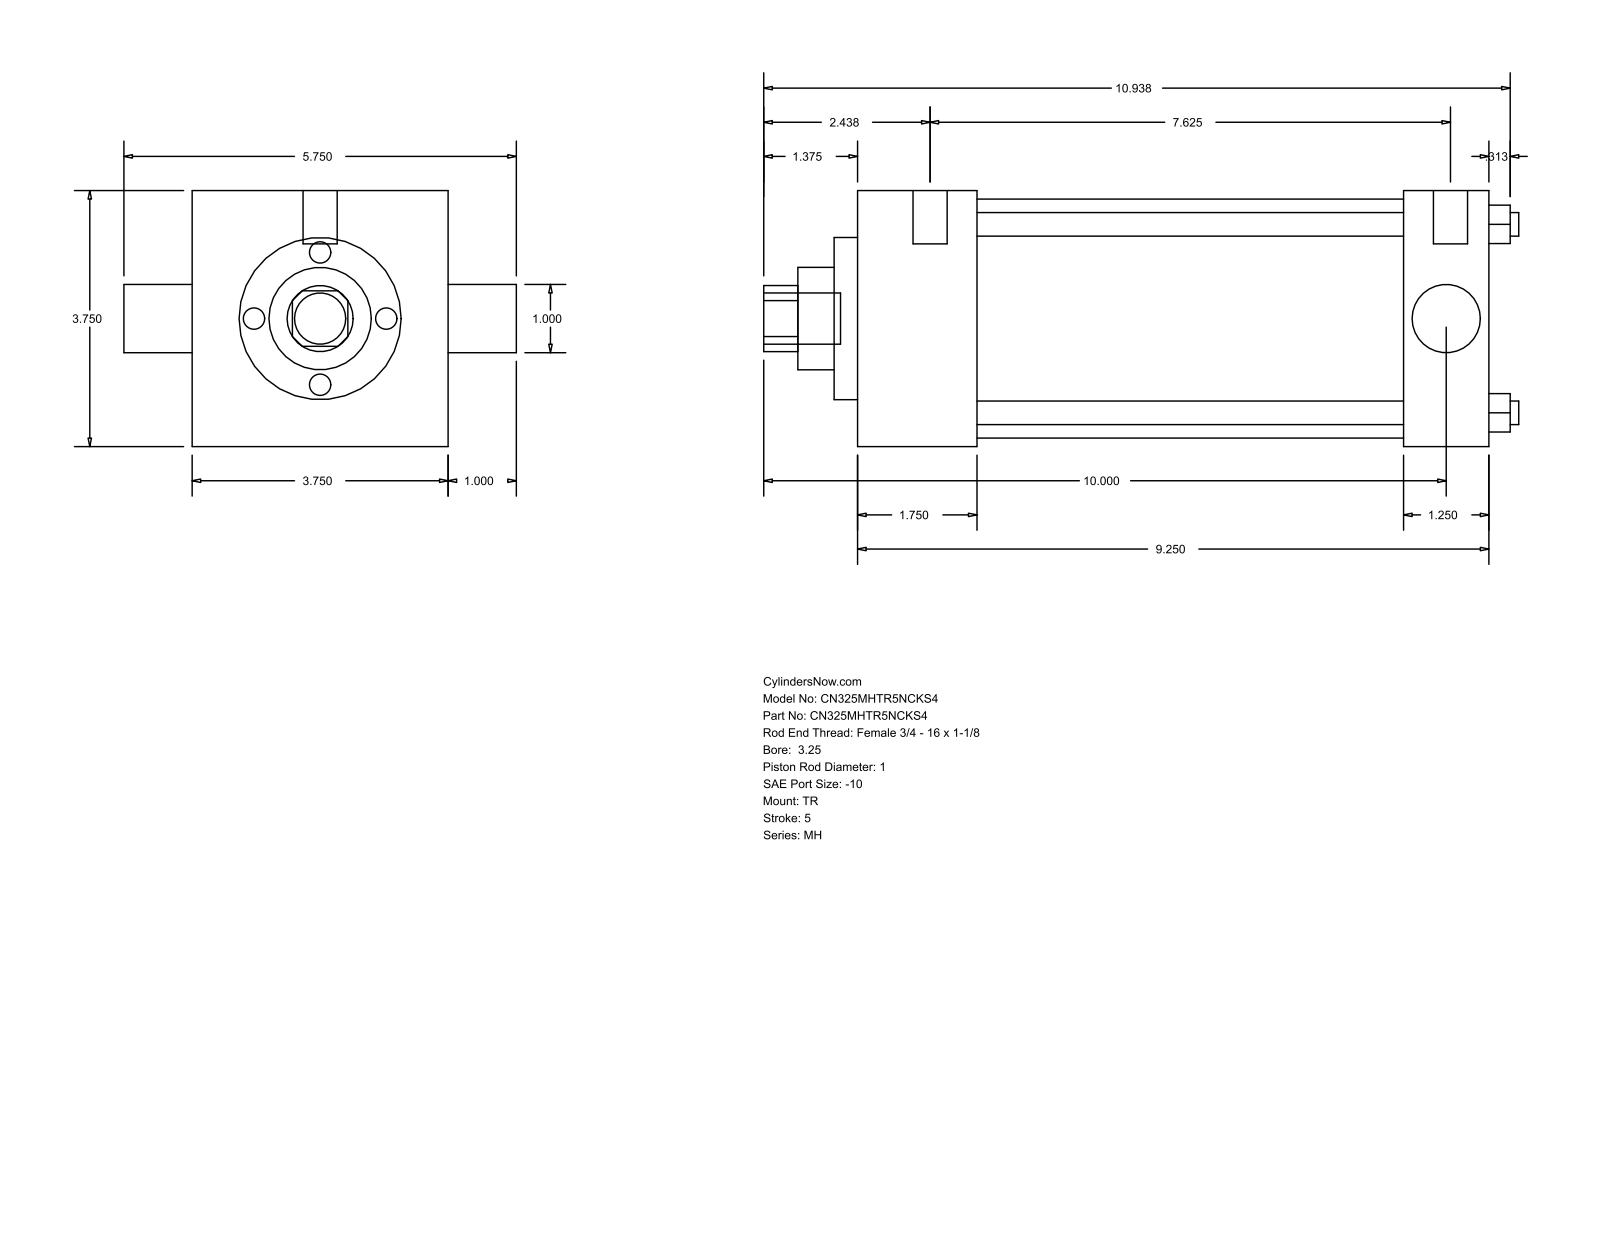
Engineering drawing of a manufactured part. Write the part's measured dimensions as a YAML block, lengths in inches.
part_name: "MH_TR__0325_1"
step_written_by: "GSSL Pune (CONFIG_CONTROL_DESIGN)"
units: inches
bodies: {solids: 0, faces: 86, planar: 61, cylindrical: 25, other: 0}
overall_size: [11.063, 5.75, 3.75]
round_holes:
  - {diameter: 0.345, count: 4}
  - {diameter: 1, count: 2}
  - {diameter: 1.5, count: 1}
  - {diameter: 2.375, count: 1}
  - {diameter: 3.5, count: 1}
round_bosses_or_shafts:
  - {diameter: 0.219, count: 3}
  - {diameter: 0.5, count: 2}
  - {diameter: 0.75, count: 1}
partial_cylinders:
  - {radius: 0.484, count: 1}
face_to_face_distances: [3.75, 9.25, 1.75, 8, 6.25, 7.5, 1.25, 0.344, 2.094, 8.344]
hole_center_spacings: [1.952, 2.76, 3.903]
